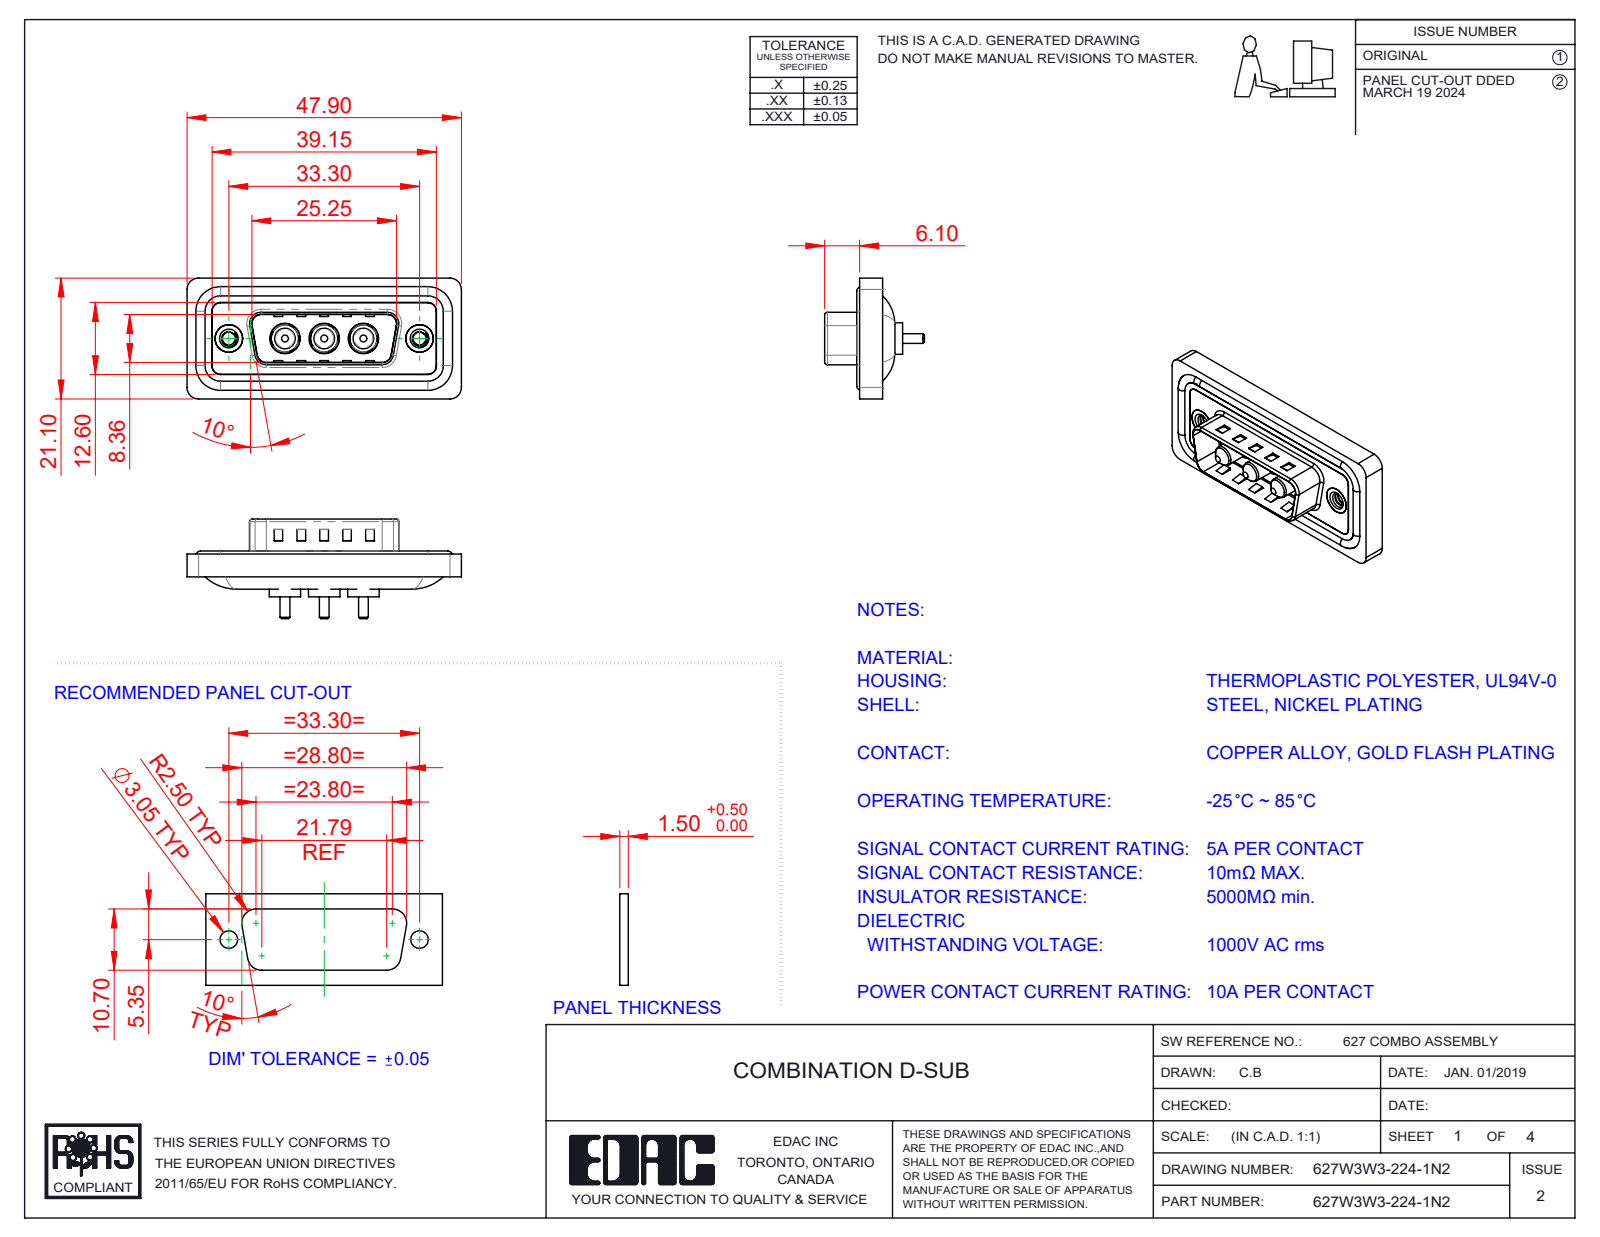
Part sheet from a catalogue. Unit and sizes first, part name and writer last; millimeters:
Units: millimetres
Overall size (bounding box): 47.9 × 21.1 × 17.4
Round holes (diameter × count): ⌀4.85 ×3, ⌀5.3 ×3, ⌀2.26 ×2, ⌀4 ×2, ⌀4.8 ×2, ⌀5 ×2
Round bosses / shafts (diameter × count): ⌀1.6 ×4, ⌀5.5 ×3, ⌀5.2 ×3, ⌀4.75 ×3, ⌀3.75 ×3, ⌀3.6 ×3, ⌀1.7 ×3, ⌀4.9 ×2
Partial cylindrical surfaces — rounded edges, fillets, slot ends (radius × count): R1.5 ×26, R2 ×20, R0.5 ×8, R1.6 ×8, R0.25 ×4, R0.6 ×4, R0.65 ×4, R0.9 ×4
Main face-to-face distances: 0.4, 1.5, 1.1, 0.5, 1.6, 3.1, 2.9, 4, 0.82, 9.58
Hole centre spacings: 6.85, 9.8, 16.65, 23.5, 13.7, 33.3
Volume: 5 542 mm³ · Surface area: 8 716 mm²
Bodies: 13 solids, 564 faces (207 planar, 241 cylindrical, 116 other)
Part name (STEP PRODUCT): 627W3W3-224-1N2; 627Combo Housing_3W3; 627Combo Shell Front_15 Contacts; Power Pin_10A S (+3 more)
STEP written by: SolidWorks 2023 (CONFIG_CONTROL_DESIGN)
